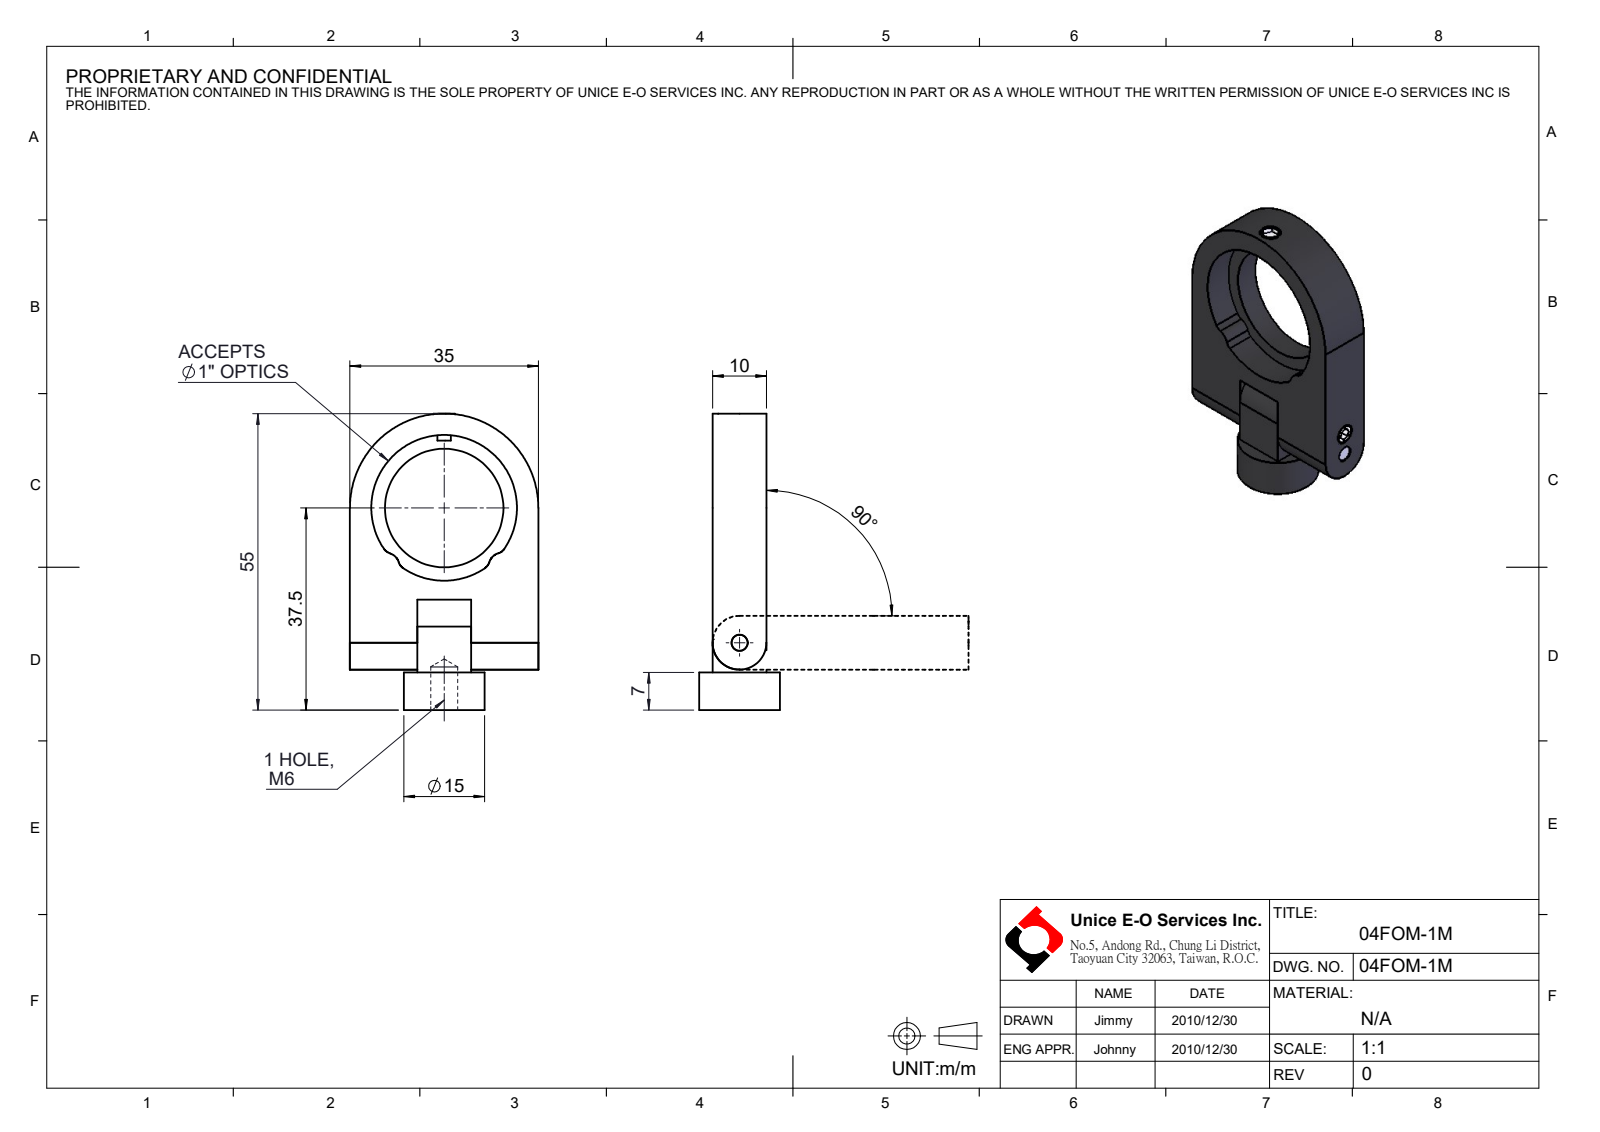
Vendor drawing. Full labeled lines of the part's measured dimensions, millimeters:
Part name (STEP PRODUCT): 04FOM-1M
STEP written by: SolidWorks 2016 (CONFIG_CONTROL_DESIGN)
Units: millimetres
Bodies: 6 solids, 94 faces (37 planar, 42 cylindrical, 15 other)
Overall size (bounding box): 55 × 35 × 15
Volume: 11 228 mm³ · Surface area: 6 753 mm²
Round holes (diameter × count): ⌀3 ×2, ⌀3.3 ×2, ⌀5 ×1, ⌀22 ×1, ⌀27 ×1
Round bosses / shafts (diameter × count): ⌀4 ×2, ⌀15 ×1, ⌀2.5 ×1
Partial cylindrical surfaces — rounded edges, fillets, slot ends (radius × count): R2 ×4, R2.5 ×2, R5 ×2, R17.5 ×1
Main face-to-face distances: 10, 12.5, 22.5, 35, 5.5, 4.5, 20.5, 7, 13.5, 4
Hole centre spacings: 2, 4.5
